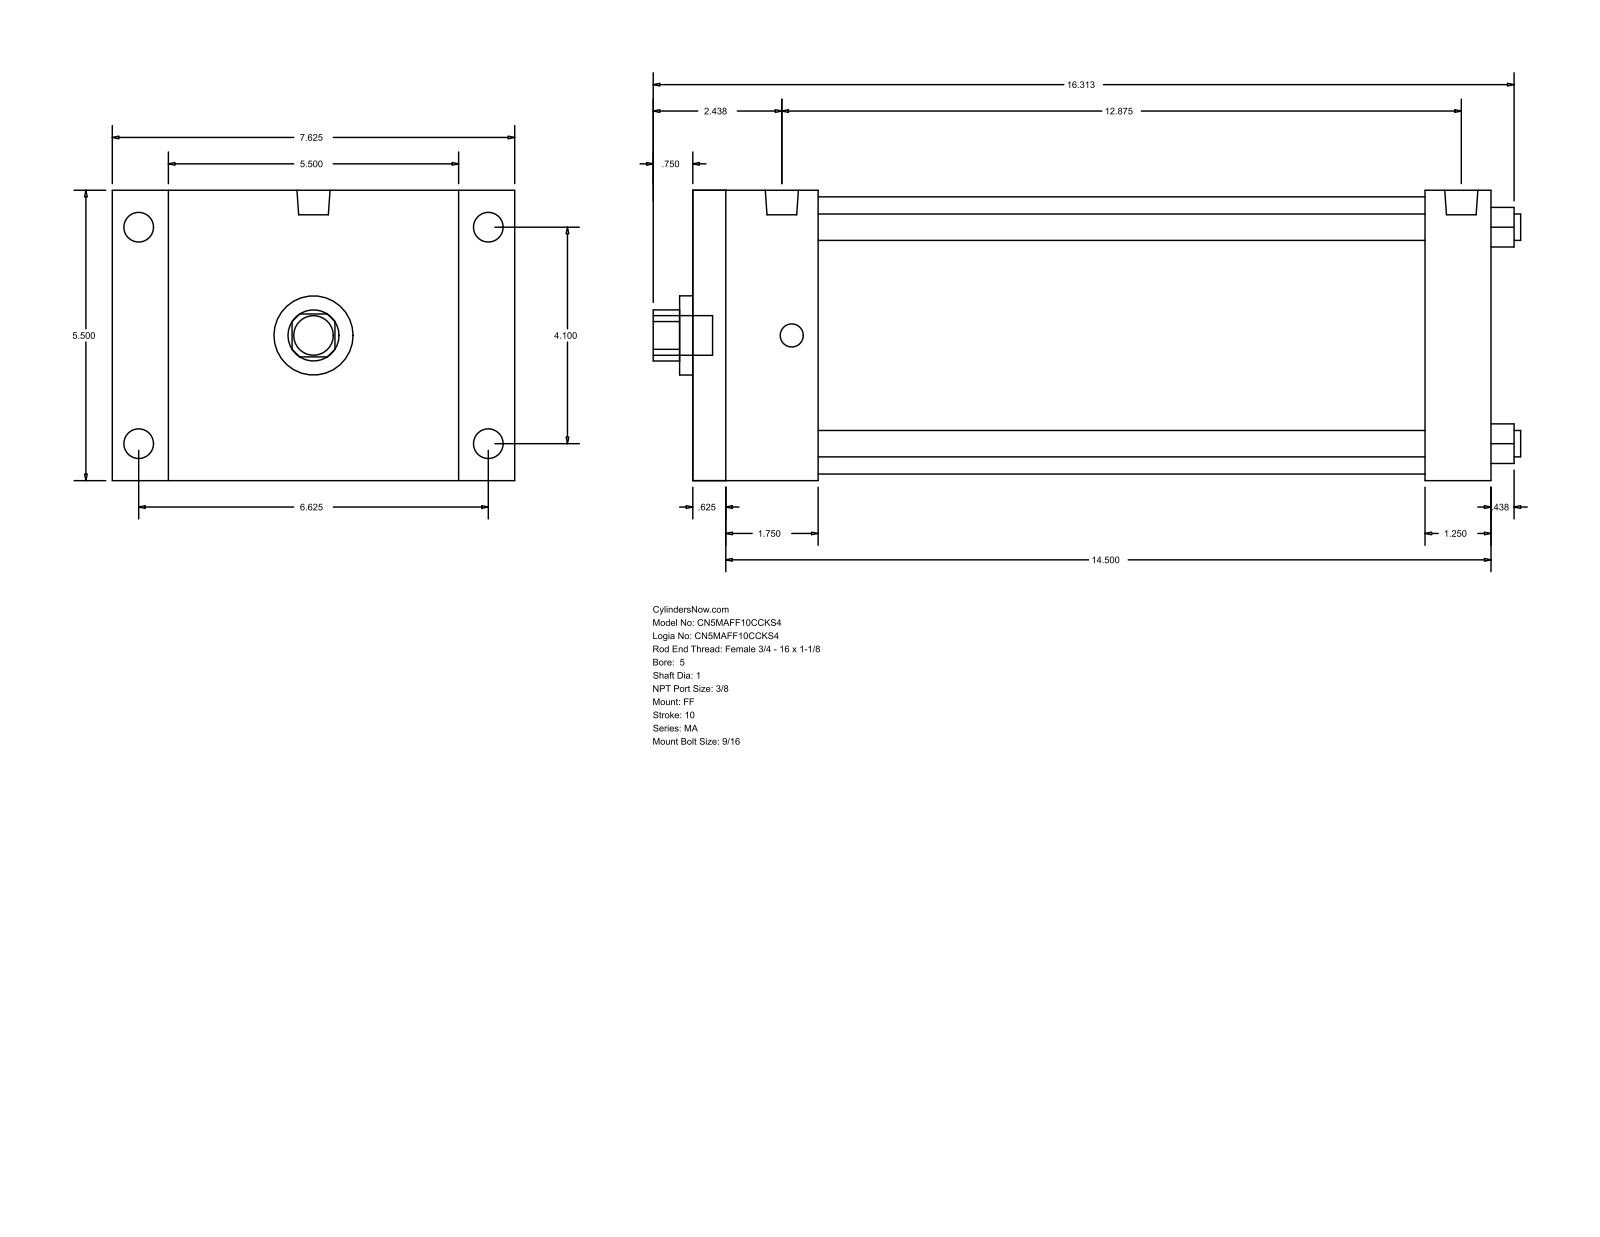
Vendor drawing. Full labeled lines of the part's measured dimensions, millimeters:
Part name (STEP PRODUCT): MA_FF__0500_1
STEP written by: GSSL Pune (CONFIG_CONTROL_DESIGN)
Units: millimetres
Bodies: 0 solids, 92 faces (64 planar, 28 cylindrical, 0 other)
Overall size (bounding box): 417.51 × 193.68 × 139.7
Round holes (diameter × count): ⌀12.7 ×4, ⌀25.4 ×1, ⌀38.1 ×1, ⌀133.35 ×1
Round bosses / shafts (diameter × count): ⌀14.29 ×4, ⌀11.11 ×4, ⌀15.93 ×2, ⌀19.05 ×1
Partial cylindrical surfaces — rounded edges, fillets, slot ends (radius × count): R12.29 ×1
Main face-to-face distances: 139.7, 384.18, 15.87, 368.31, 352.43, 336.56, 31.75, 60.33, 44.46, 292.1
Hole centre spacings: 73.64, 104.14, 147.28
